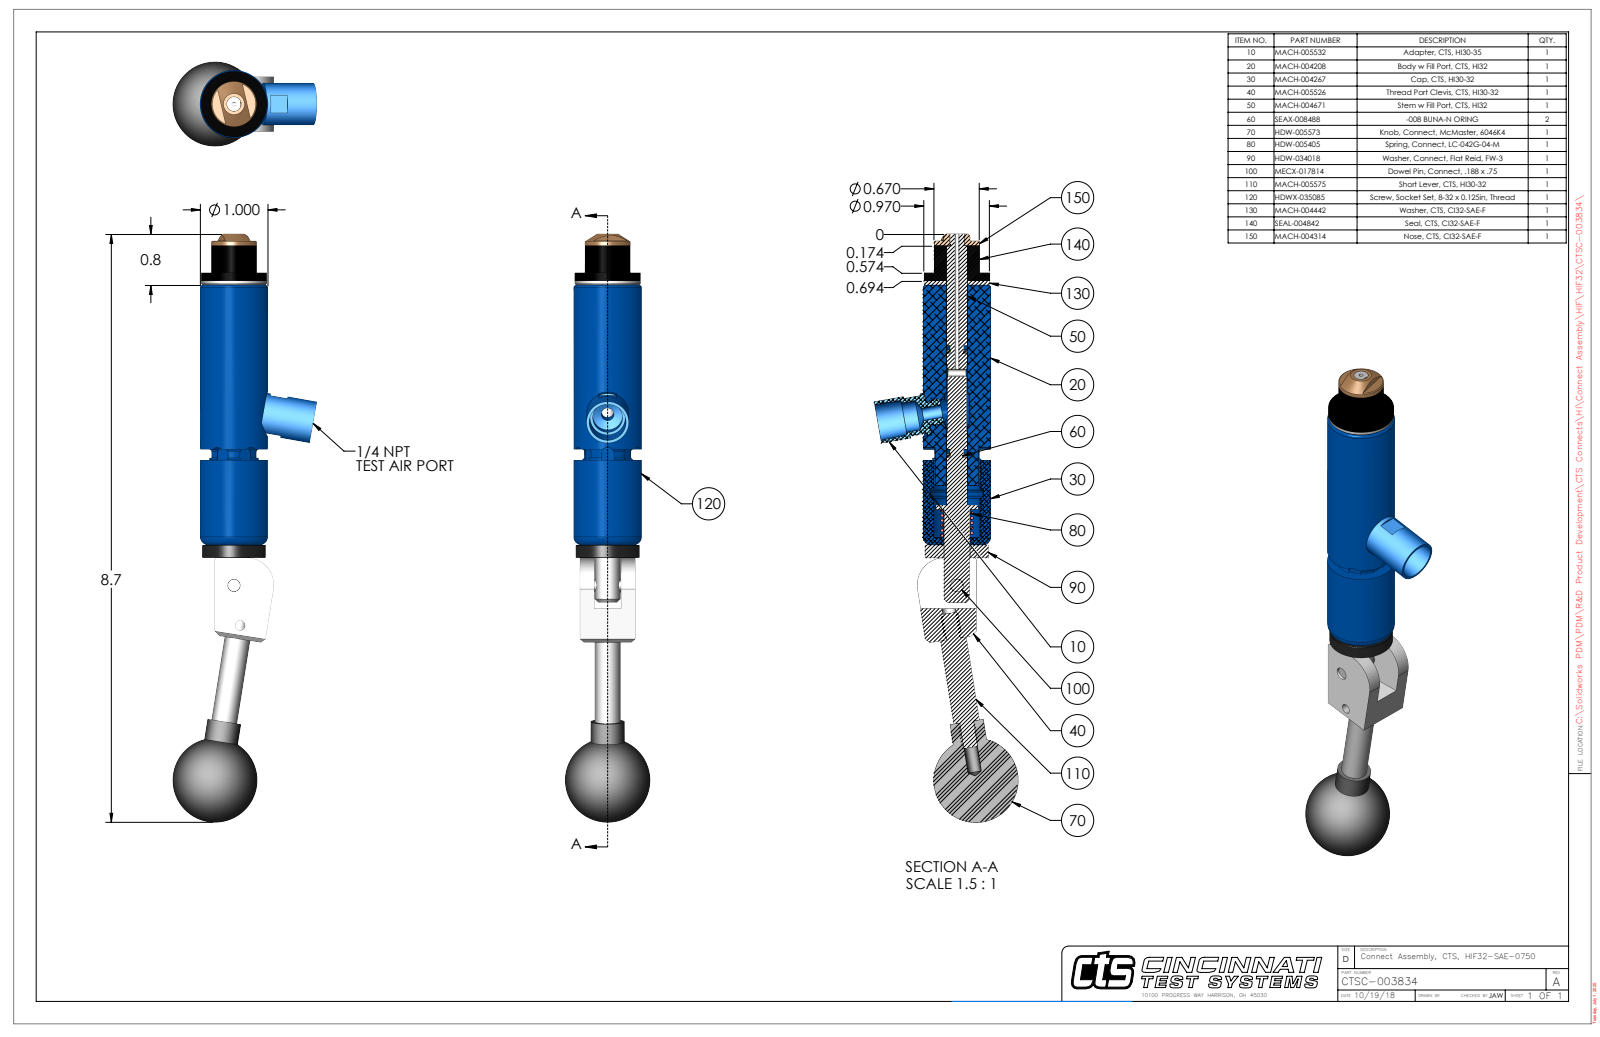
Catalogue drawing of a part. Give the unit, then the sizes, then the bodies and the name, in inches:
Units: inches
Overall size (bounding box): 8.692 × 2.128 × 1.25
Round holes (diameter × count): ⌀0.201 ×2, ⌀0.063 ×1, ⌀0.109 ×1, ⌀0.136 ×1, ⌀0.15 ×1, ⌀0.187 ×1, ⌀0.189 ×1, ⌀0.213 ×1, ⌀0.31 ×1, ⌀0.314 ×1, ⌀0.316 ×1, ⌀0.385 ×1
Round bosses / shafts (diameter × count): ⌀0.25 ×2, ⌀0.201 ×2, ⌀1 ×1, ⌀0.97 ×1, ⌀0.936 ×1, ⌀0.67 ×1, ⌀0.62 ×1, ⌀0.5 ×1
Partial cylindrical surfaces — rounded edges, fillets, slot ends (radius × count): R0.093 ×6, R0.029 ×2, R0.079 ×1, R0.325 ×1, R0.375 ×1, R0.4 ×1, R0.472 ×1
Main face-to-face distances: 0.06, 0.21, 0.602, 3.9, 3.841, 0.812, 4.088, 4.028, 0.187, 0.52
Hole centre spacings: 0.599, 1.658, 2.252
Volume: 5.264 in³ · Surface area: 41.78 in²
Bodies: 9 solids, 304 faces (112 planar, 127 cylindrical, 65 other)
Part name (STEP PRODUCT): CTSC-003834
STEP written by: SolidWorks 2023 (AUTOMOTIVE_DESIGN)
